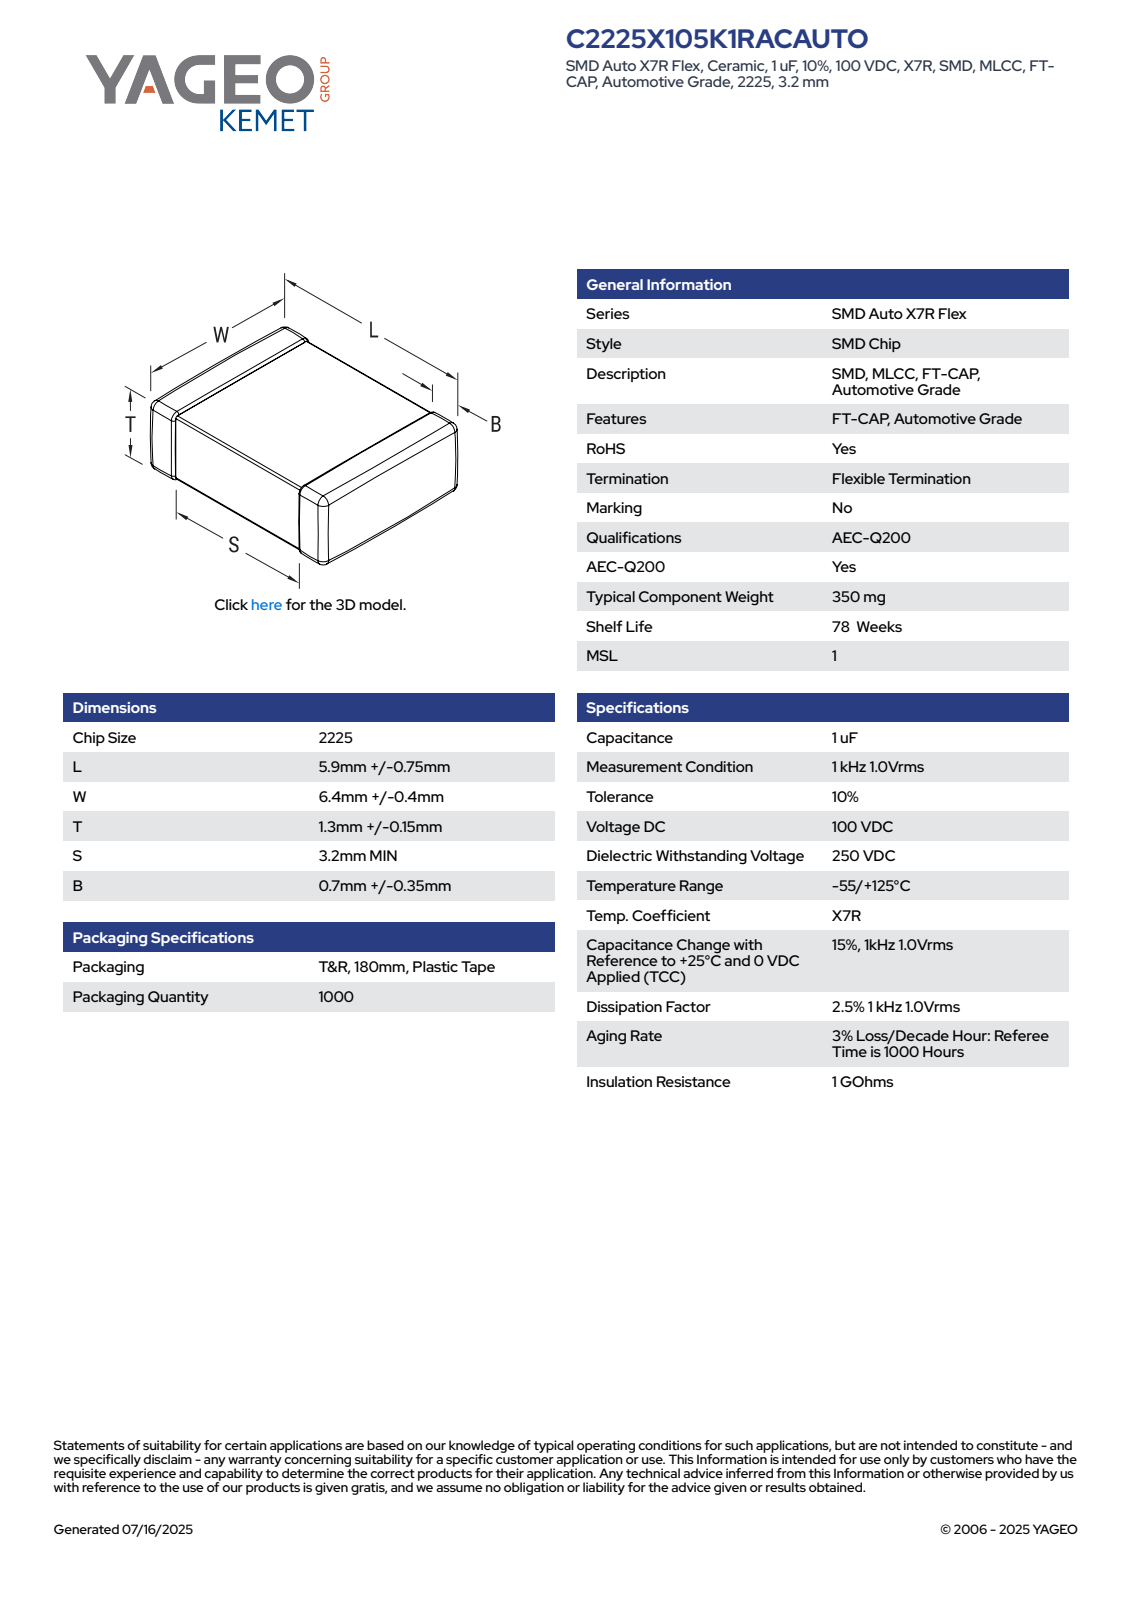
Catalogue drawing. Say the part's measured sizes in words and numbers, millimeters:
The part is named "CCS_CCSTD_2225_L6.65W6.8T1.45B0.7". Its 3-D file was written by "SolidWorks 2021 (AUTOMOTIVE_DESIGN)". It is 4 solids with 121 faces: 71 planar, 34 cylindrical and 16 other. Overall it measures 6.8 by 6.65 by 1.45 millimeters. Its volume is 55 cubic millimeters and its surface area 129 square millimeters. Partial cylindrical surfaces (rounded edges, fillets, slot ends): 24 of radius 0.14. The main face-to-face distances are 1.17, 1.31, 1.45, 6.65, 6.52, 6.66, 6.8, 1, 2.59, 4.06.
